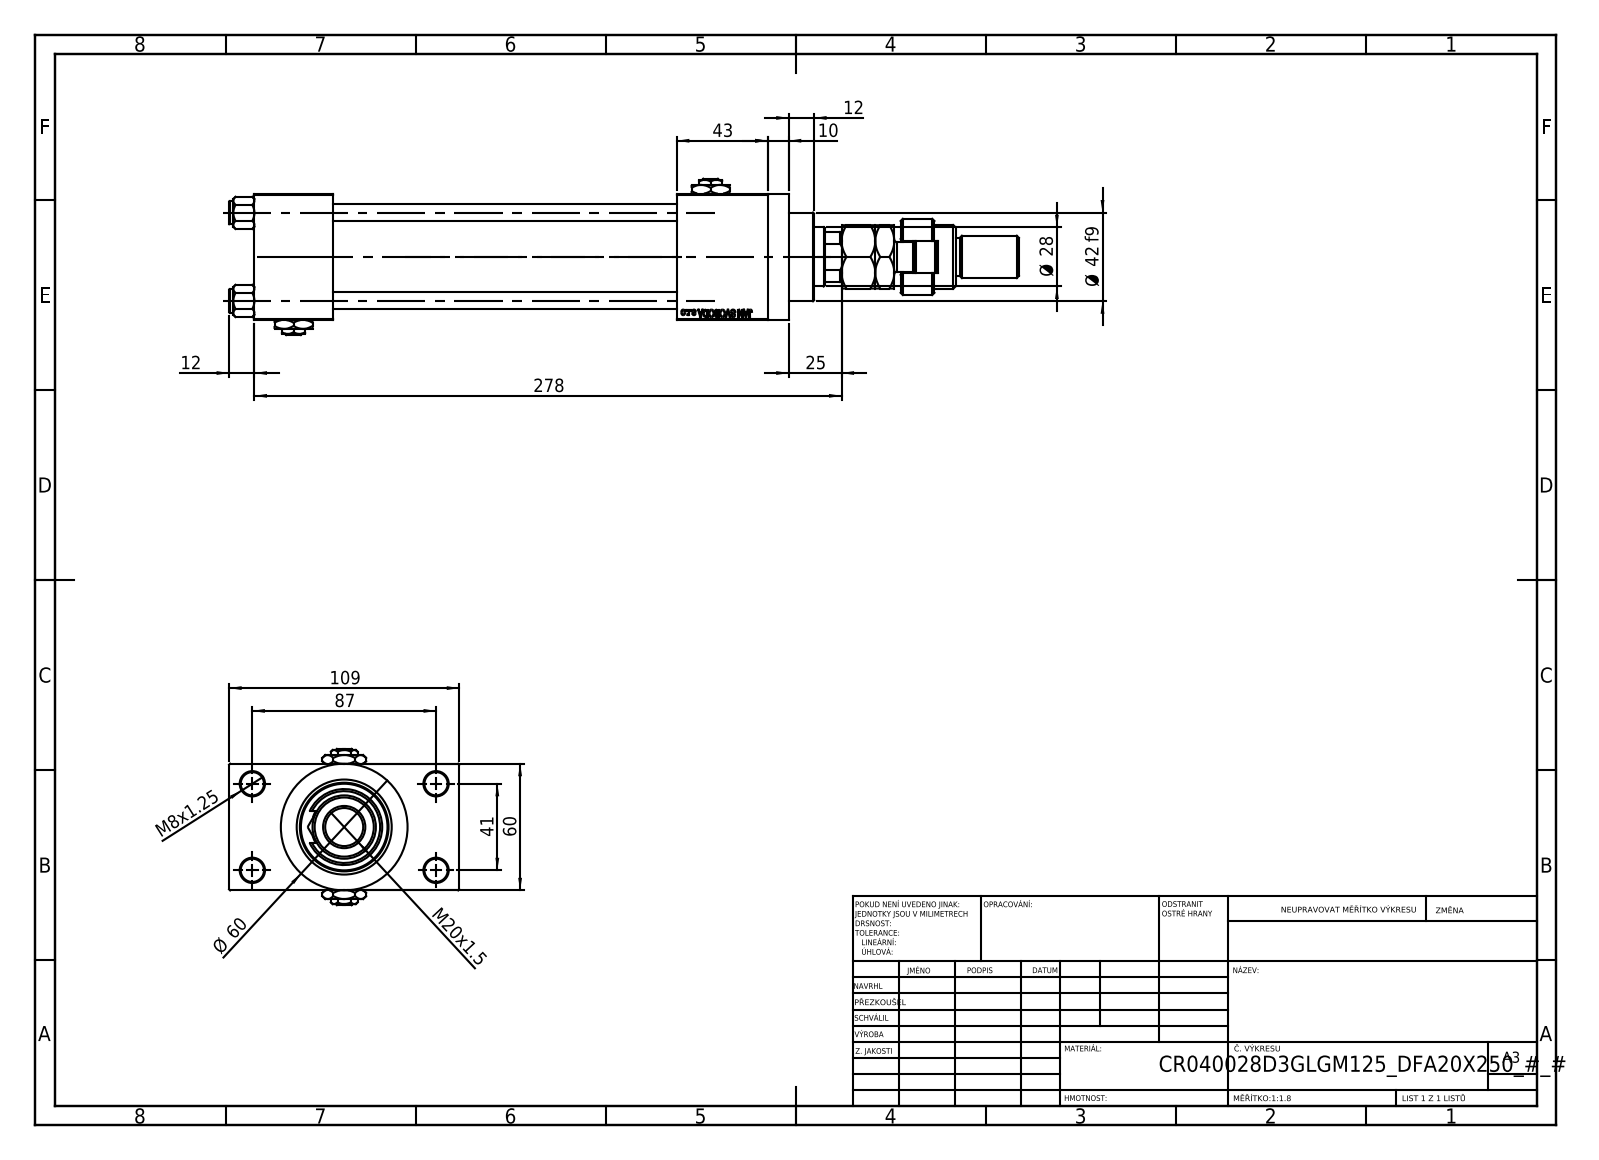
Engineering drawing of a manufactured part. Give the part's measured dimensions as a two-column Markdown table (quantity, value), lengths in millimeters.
| quantity | value |
| --- | --- |
| part name | NUT_M5_D; V215CR_D_Body; Zatka_pro_OIL_PORT; MFA (+4 more) |
| STEP written by | SolidWorks 2019 (CONFIG_CONTROL_DESIGN) |
| units | millimeters |
| bodies | 15 solids, 1274 faces (570 planar, 102 cylindrical, 602 other) |
| overall size | 374 × 109 × 74 |
| volume | 714 263 mm³ |
| surface area | 191 038 mm² |
| round holes (diameter × count) | 8 × 4, 11 × 4, 7 × 2, 16.66 × 2, 24 × 2, 18.5 × 1, 28 × 1, 31 × 1, 40 × 1, 45 × 1 |
| round bosses / shafts (diameter × count) | 11 × 4, 60 × 1, 46 × 1, 42 × 1, 36 × 1, 30 × 1, 22 × 1, 20 × 1 |
| partial cylindrical surfaces (radius × count) | 7.5 × 1, 12 × 1, 13.5 × 1 |
| main face-to-face distances | 60, 24.5, 84.5, 163, 37, 200, 43, 243, 206, 109 |
| hole center spacings | 22.65, 29.49, 41.7, 47.15, 48.09, 64.35, 76.49, 41 |
